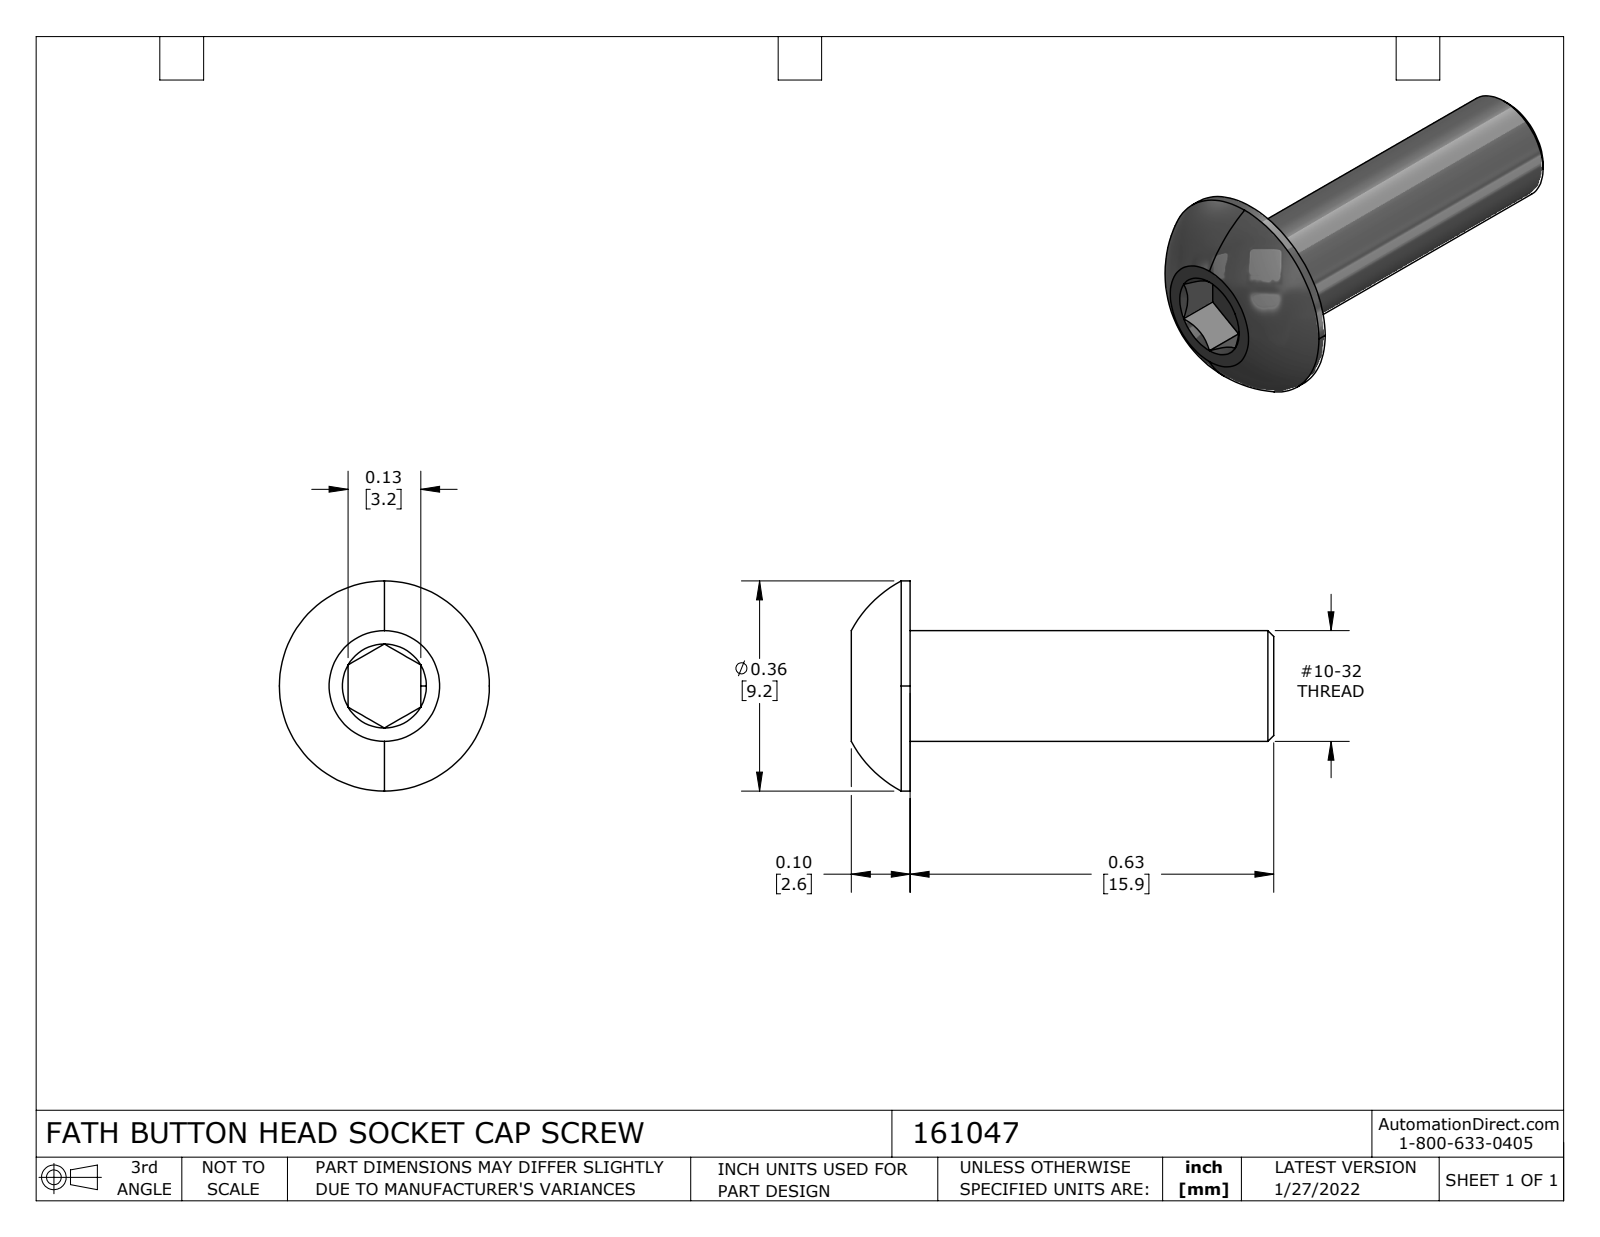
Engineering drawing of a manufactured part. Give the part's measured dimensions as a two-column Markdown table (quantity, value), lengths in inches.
| quantity | value |
| --- | --- |
| part name | 161047 |
| STEP written by | SolidWorks 2021 (CONFIG_CONTROL_DESIGN) |
| units | inches |
| bodies | 1 solid, 29 faces (12 planar, 4 cylindrical, 13 other) |
| overall size | 0.726 × 0.361 × 0.361 |
| volume | 0.024 in³ |
| surface area | 0.656 in² |
| round bosses / shafts (diameter × count) | 0.361 × 1, 0.19 × 1 |
| main face-to-face distances | 0.625, 0.125, 0.655, 0.03, 0.726, 0.101, 0.071, 0.063 |
